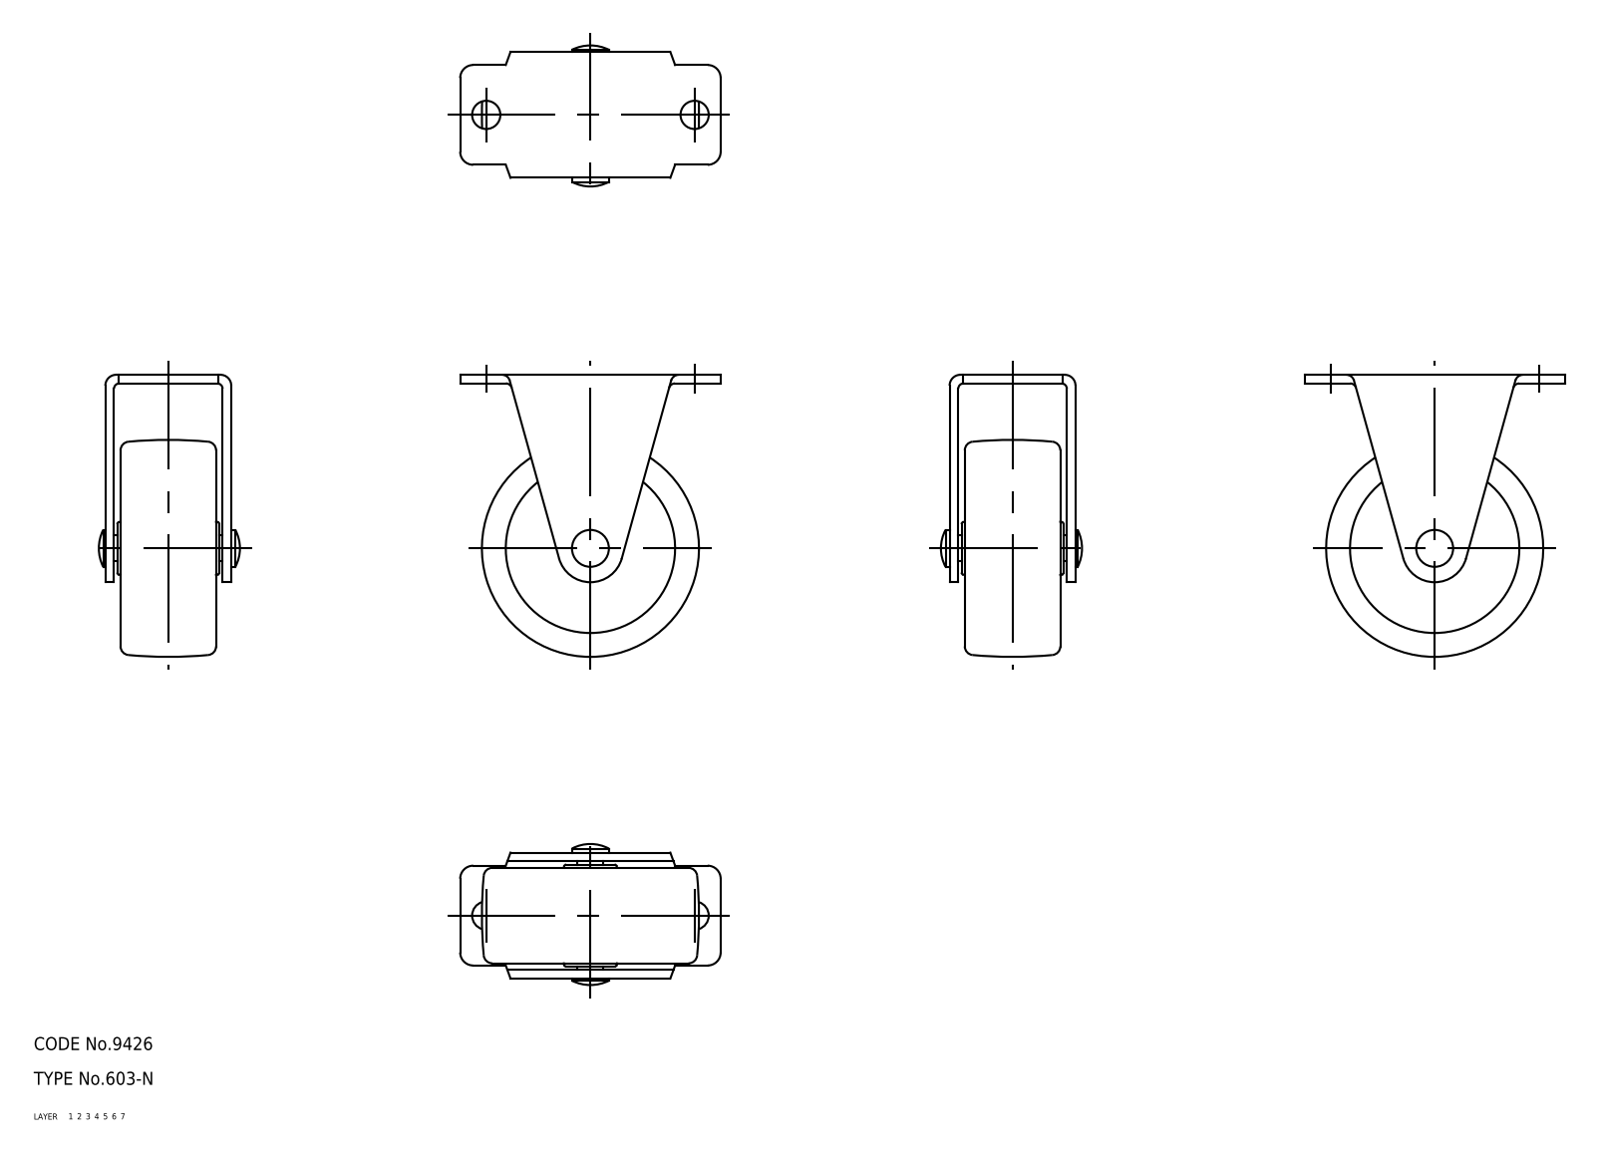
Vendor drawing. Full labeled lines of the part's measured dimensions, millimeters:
Part name (STEP PRODUCT): wheel; axle; No_603_N_14234_36
STEP written by: CADfix (AUTOMOTIVE_DESIGN)
Units: millimetres
Bodies: 3 solids, 113 faces (0 planar, 0 cylindrical, 113 other)
Overall size (bounding box): 65 × 60 × 32.5
Volume: 33 265 mm³ · Surface area: 18 300 mm²
